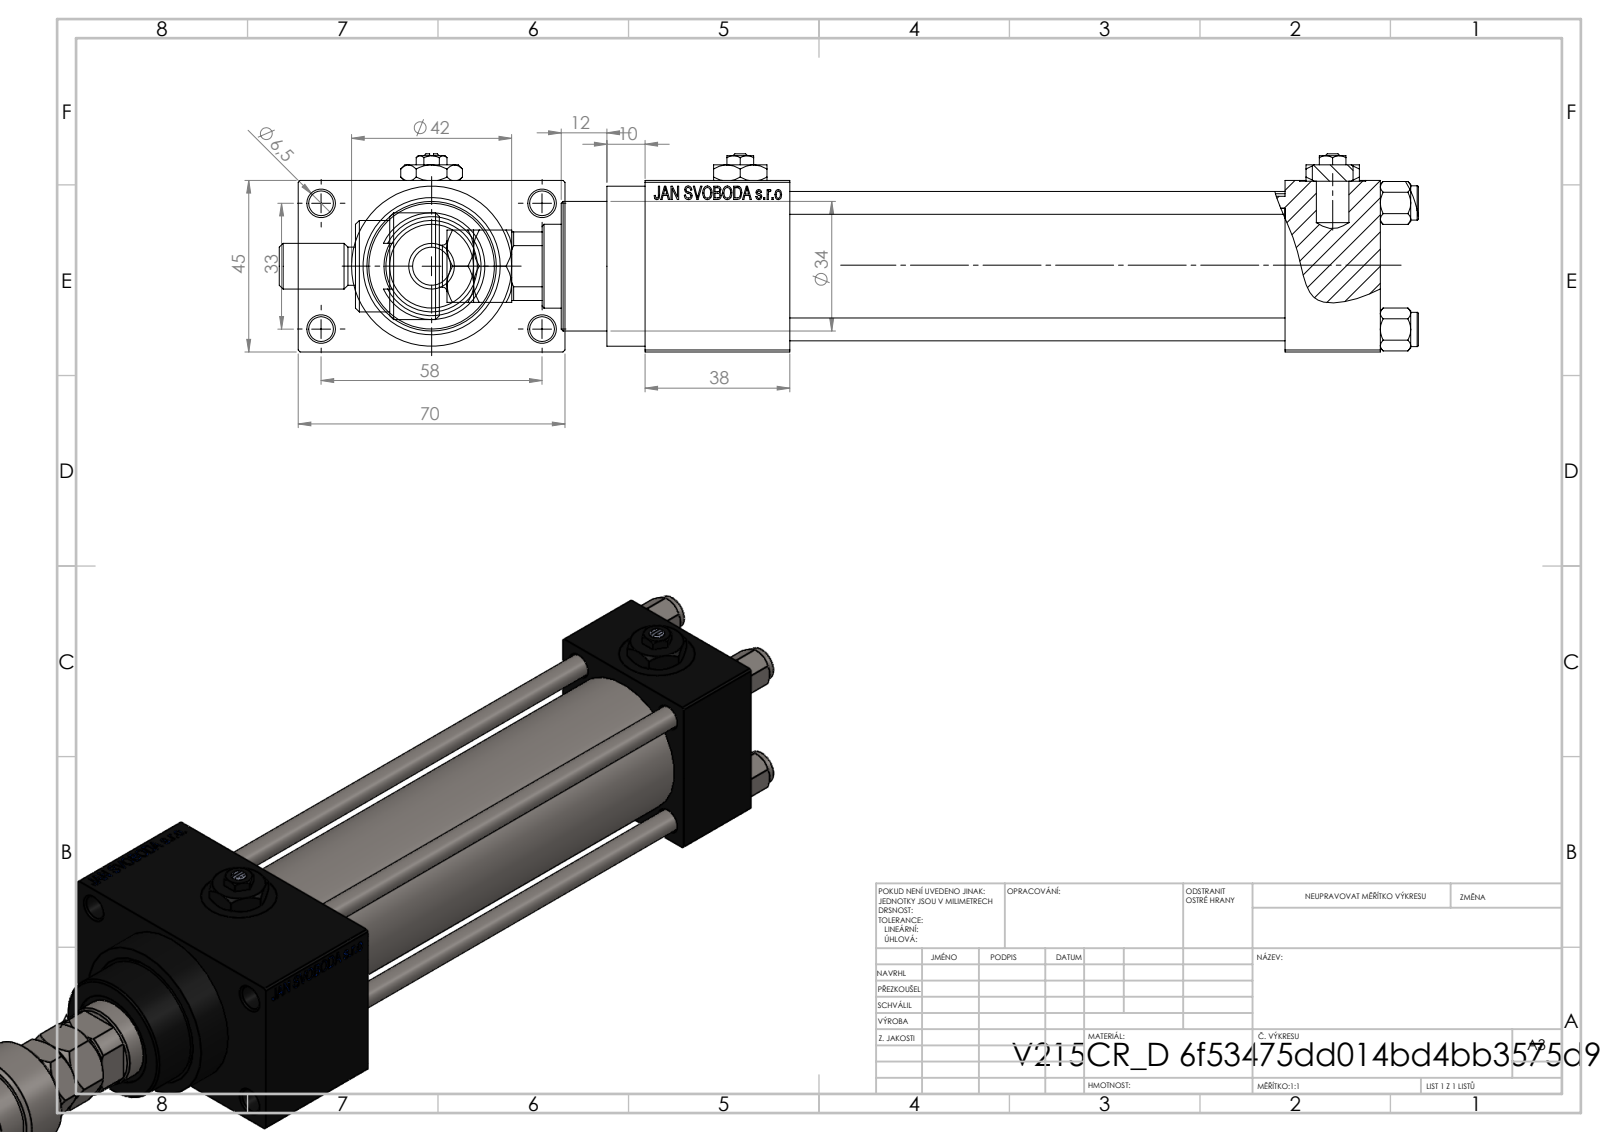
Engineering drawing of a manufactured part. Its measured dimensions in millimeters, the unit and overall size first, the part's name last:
Units: millimetres
Overall size (bounding box): 299 × 70 × 52
Round holes (diameter × count): ⌀6 ×4, ⌀6.5 ×4, ⌀13.16 ×4, ⌀20 ×4, ⌀7 ×3, ⌀10.5 ×1, ⌀22 ×1, ⌀24 ×1, ⌀25 ×1, ⌀32 ×1, ⌀33 ×1
Round bosses / shafts (diameter × count): ⌀9 ×4, ⌀42 ×1, ⌀38 ×1, ⌀34 ×1, ⌀28 ×1, ⌀18 ×1, ⌀12 ×1, ⌀11 ×1
Partial cylindrical surfaces — rounded edges, fillets, slot ends (radius × count): R9.75 ×1, R10.5 ×1
Main face-to-face distances: 45, 25, 12.5, 130, 155, 57.5, 38, 168, 193, 70
Hole centre spacings: 12.4, 23.48, 33.2, 33.37, 35.35, 45.6, 56.35, 33
Volume: 325 353 mm³ · Surface area: 117 900 mm²
Bodies: 15 solids, 1288 faces (570 planar, 112 cylindrical, 606 other)
Part name (STEP PRODUCT): V215CR_D_TYCINKA; MFA; V215CR_D_Body; FEMALE_PART_FOR_DFA (+4 more)
STEP written by: SolidWorks 2019 (CONFIG_CONTROL_DESIGN)
